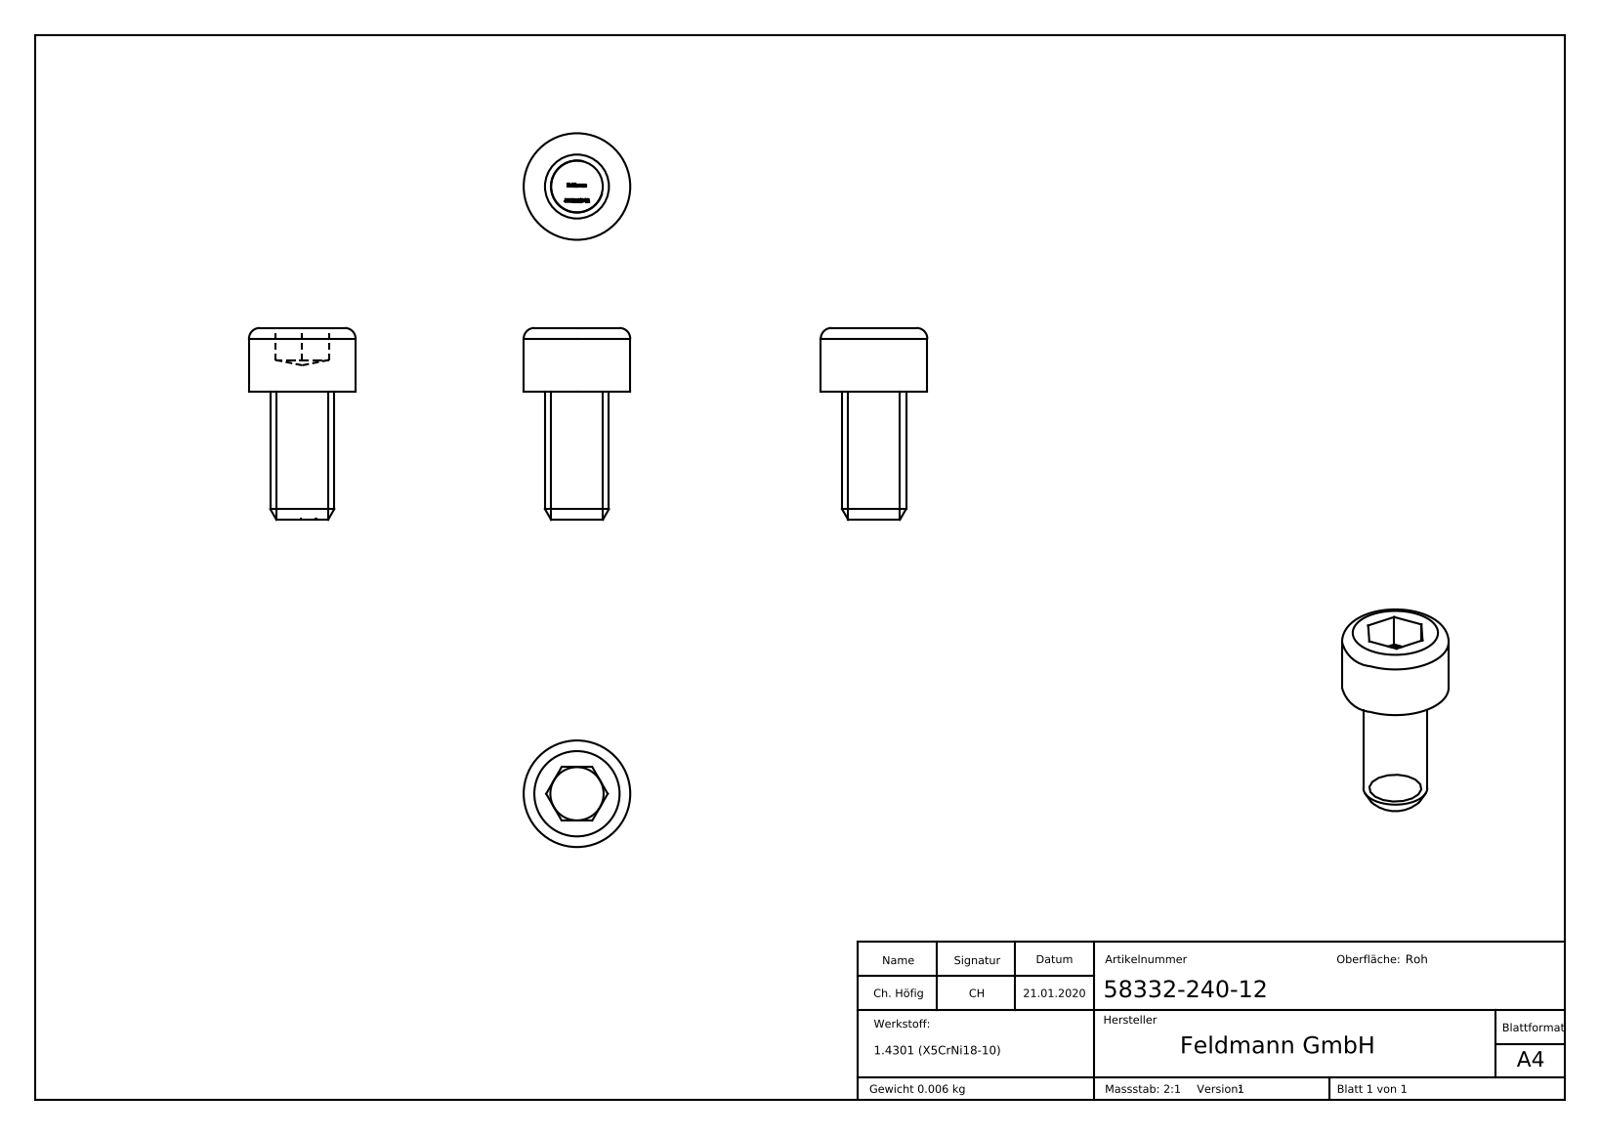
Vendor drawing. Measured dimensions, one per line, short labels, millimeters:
name: 58332-240-12
written by: SolidWorks 2015 (CONFIG_CONTROL_DESIGN)
unit: mm
bodies: 1 solid, 286 faces (153 planar, 2 cylindrical, 131 other)
size: 91.9 × 10 × 10
volume: 731 mm³; area: 603 mm²
bosses: 1× ⌀10, 1× ⌀6
face distances: 6, 5, 12, 18, 3, 15, 11.9, 14.9, 17.9, 0.33
